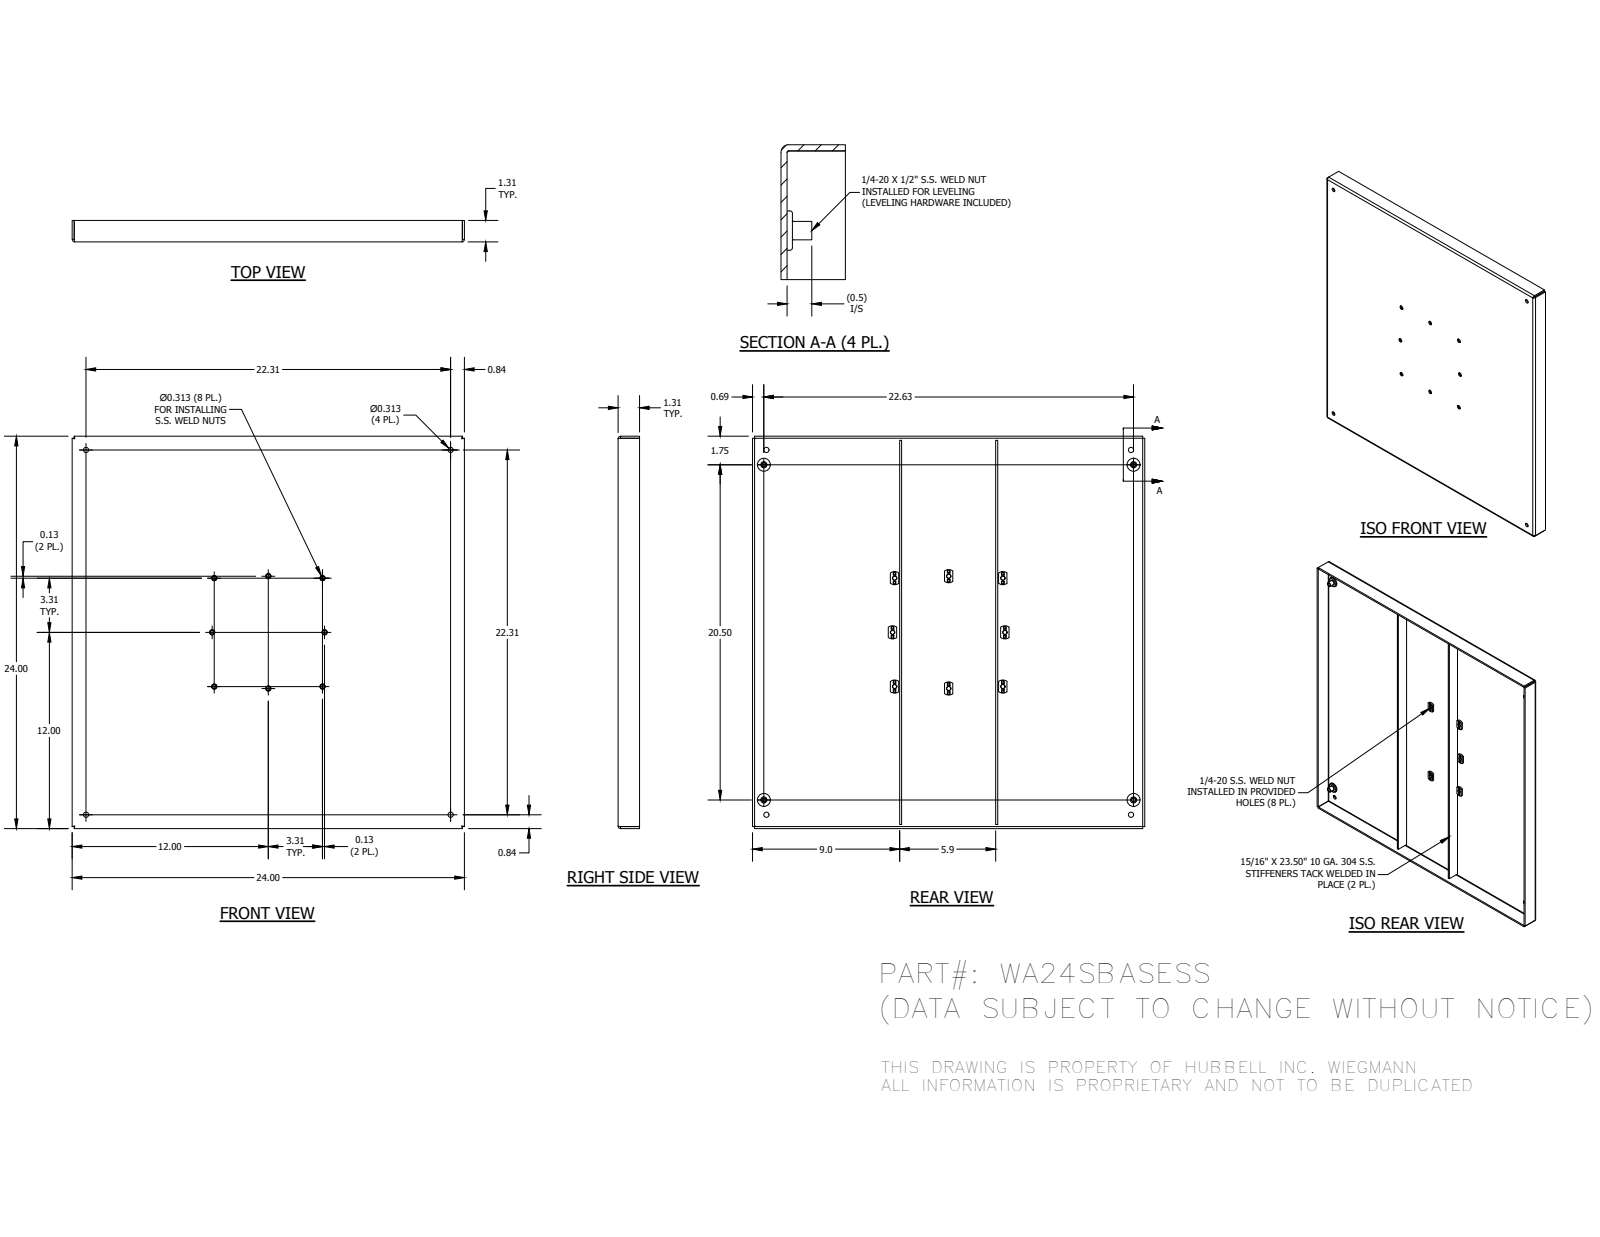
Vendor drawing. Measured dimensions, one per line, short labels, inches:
name: WA24SBASEBSS; WA24SBASESSSTFNR; 349122; HFW349157 (+1 more)
written by: Autodesk Inventor 2016 (AUTOMOTIVE_DESIGN)
unit: in
bodies: 15 solids, 346 faces (210 planar, 80 cylindrical, 56 other)
size: 24 × 24 × 1.313
volume: 91.66 in³; area: 1 500 in²
holes: 12× ⌀0.25, 12× ⌀0.313
bosses: 8× ⌀0.297, 4× ⌀0.8, 4× ⌀0.375
rounds: 10× R0.096, 8× R0.406, 4× R0.031, 4× R0.156
face distances: 0.125, 23.875, 9, 14.875, 24, 23.75, 9.125, 15, 8.875, 14.75
hole spacings: 3.315, 7.519, 13.566, 16.458, 18.37, 0.92, 4.861, 6.625
